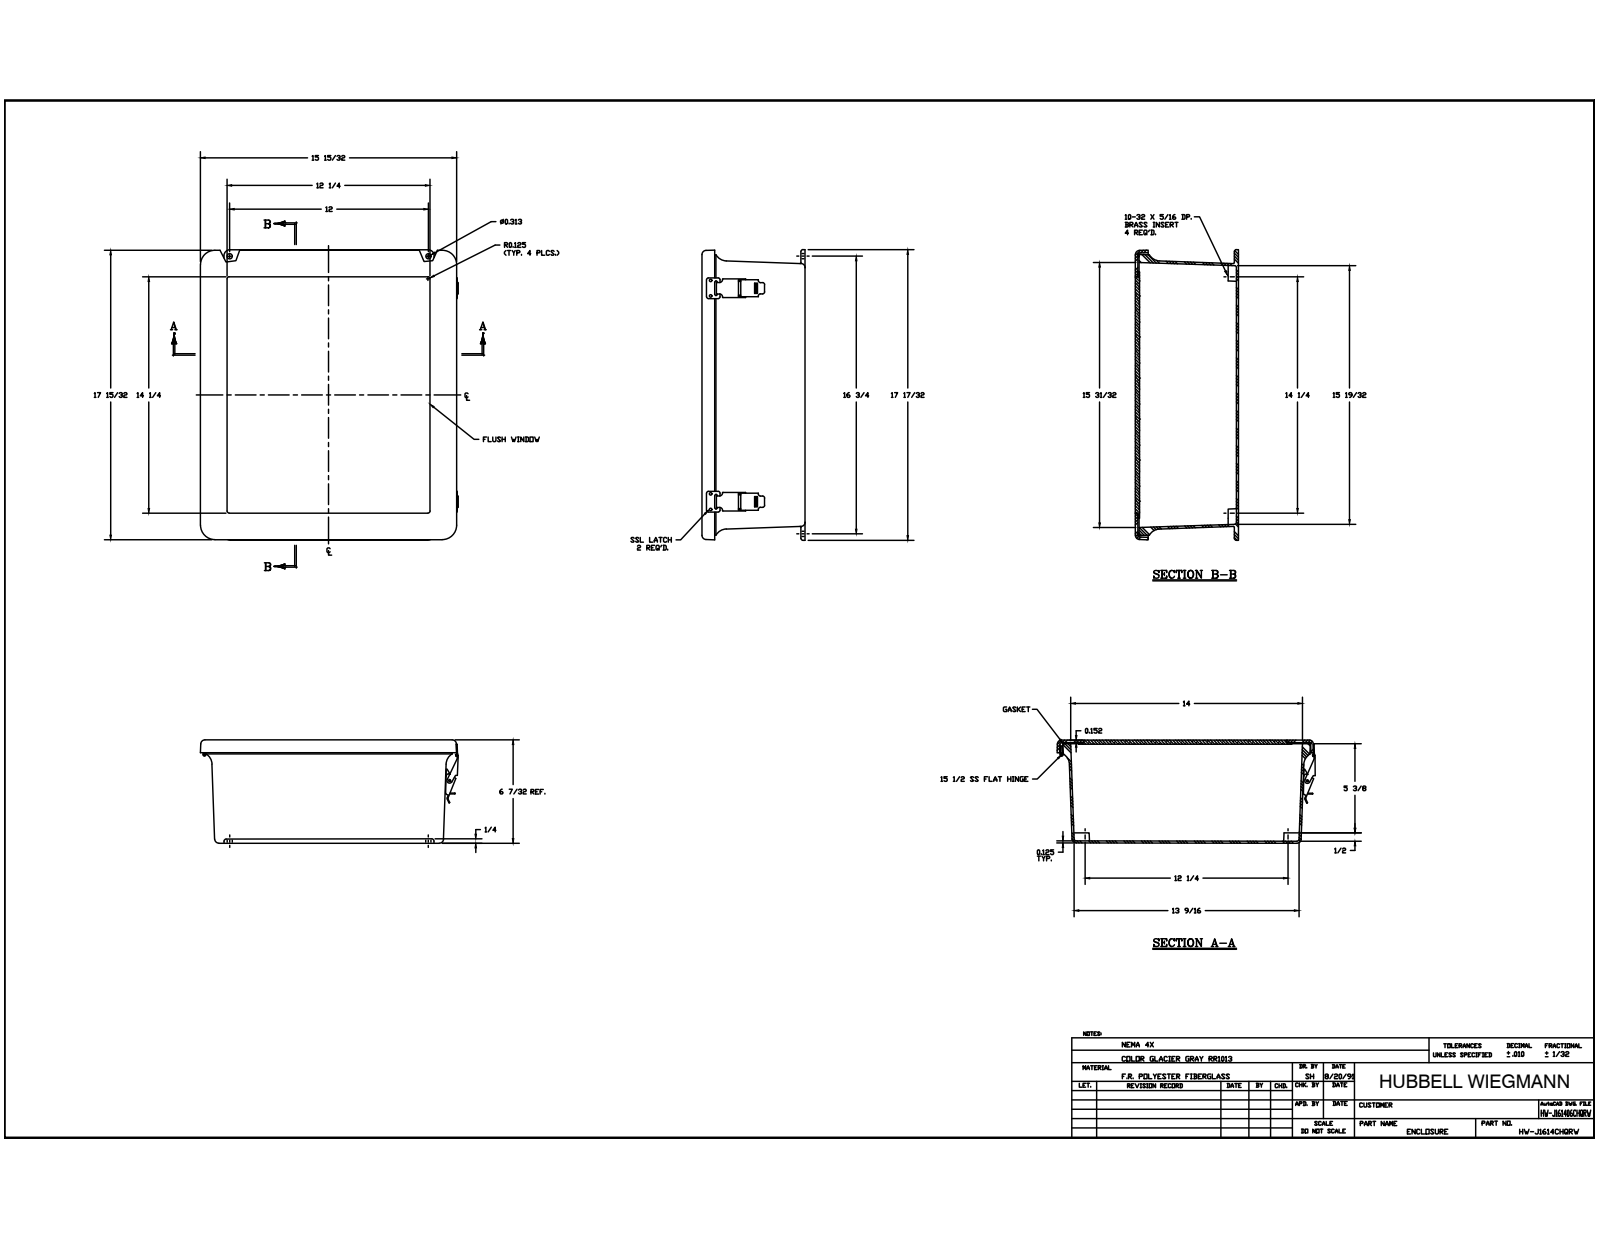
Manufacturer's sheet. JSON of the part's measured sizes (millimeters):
{"part_name": "J1614HL_4; RMINS45821P_87; RMINS45821P_88; RMINS45821P_89 (+8 more)", "step_written_by": "Autodesk Inventor 2014 (AUTOMOTIVE_DESIGN)", "units": "millimeters", "bodies": {"solids": 41, "faces": 1113, "planar": 496, "cylindrical": 468, "other": 149}, "overall_size": [445.29, 396, 157.71], "volume_mm3": 2672000, "surface_area_mm2": 1306000, "round_holes": [[3.56, 22], [3.33, 10], [2.64, 8], [3.86, 8], [3.3, 4], [3.96, 4], [5.54, 4], [3.43, 2], [9.52, 2], [2.16, 1]], "round_bosses_or_shafts": [[3.17, 18], [6.35, 10], [6.86, 4], [7.62, 1], [4.31, 1], [3.94, 1], [3.05, 1]], "partial_cylinders_radius": [[3.17, 24], [0.38, 20], [0.79, 20], [1.14, 16], [6.35, 16], [0.76, 12], [0.57, 9], [1.52, 6]], "face_to_face_distances": [3.18, 157.71, 6.35, 151.36, 154.53, 148.18, 3.86, 3.17, 153.85, 150.67], "hole_center_spacings": [95.25, 190.5, 326.86, 23.81, 326.84, 19.05, 285.75, 327.39]}
